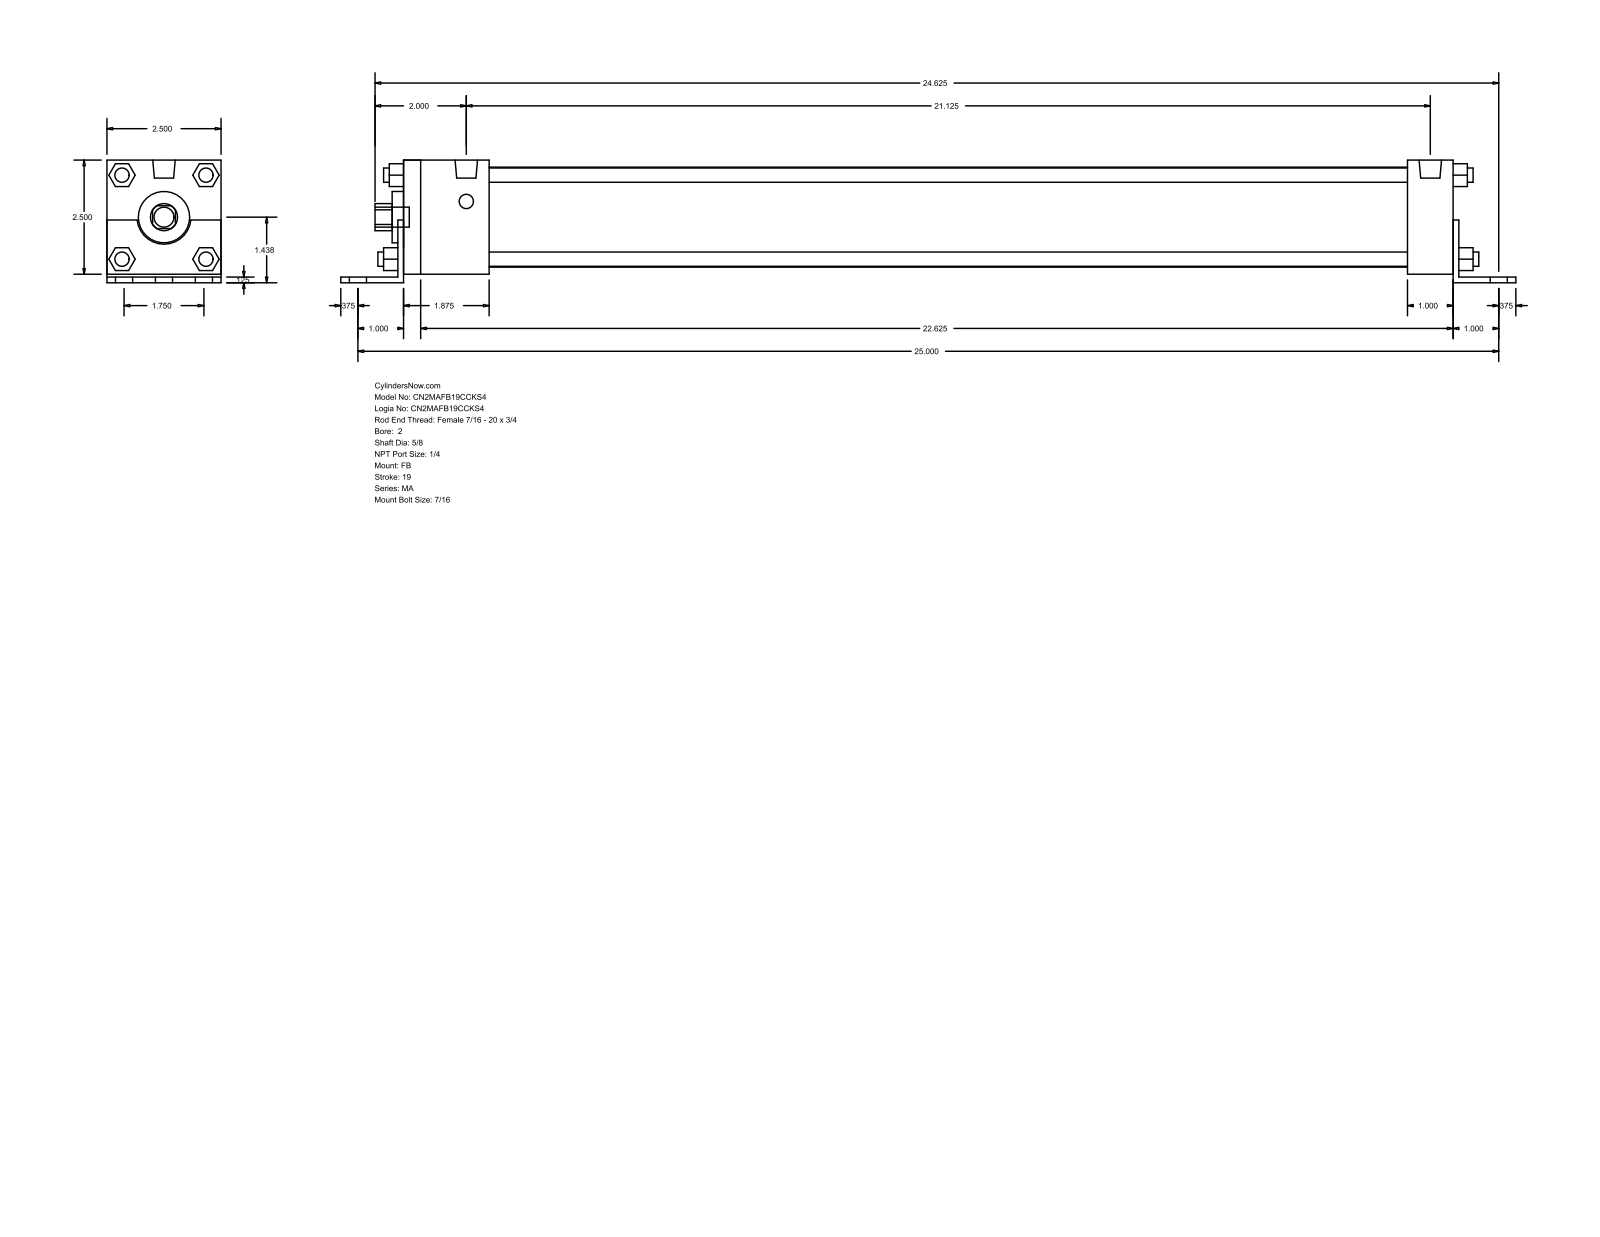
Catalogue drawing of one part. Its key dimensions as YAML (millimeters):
part_name: "MA_FB__0200_0.625"
step_written_by: "GSSL Pune (CONFIG_CONTROL_DESIGN)"
units: millimeters
bodies: {solids: 0, faces: 140, planar: 105, cylindrical: 35, other: 0}
overall_size: [654.05, 68.26, 63.5]
round_holes:
  - {diameter: 15.88, count: 1}
  - {diameter: 28.57, count: 1}
  - {diameter: 55.63, count: 1}
round_bosses_or_shafts:
  - {diameter: 7.94, count: 8}
  - {diameter: 11.11, count: 7}
  - {diameter: 12.49, count: 2}
partial_cylinders:
  - {radius: 7.54, count: 1}
  - {radius: 15.05, count: 1}
face_to_face_distances: [63.5, 3.17, 4.76, 68.26, 1.59, 65.09, 584.2, 590.55, 3.18, 587.37]
